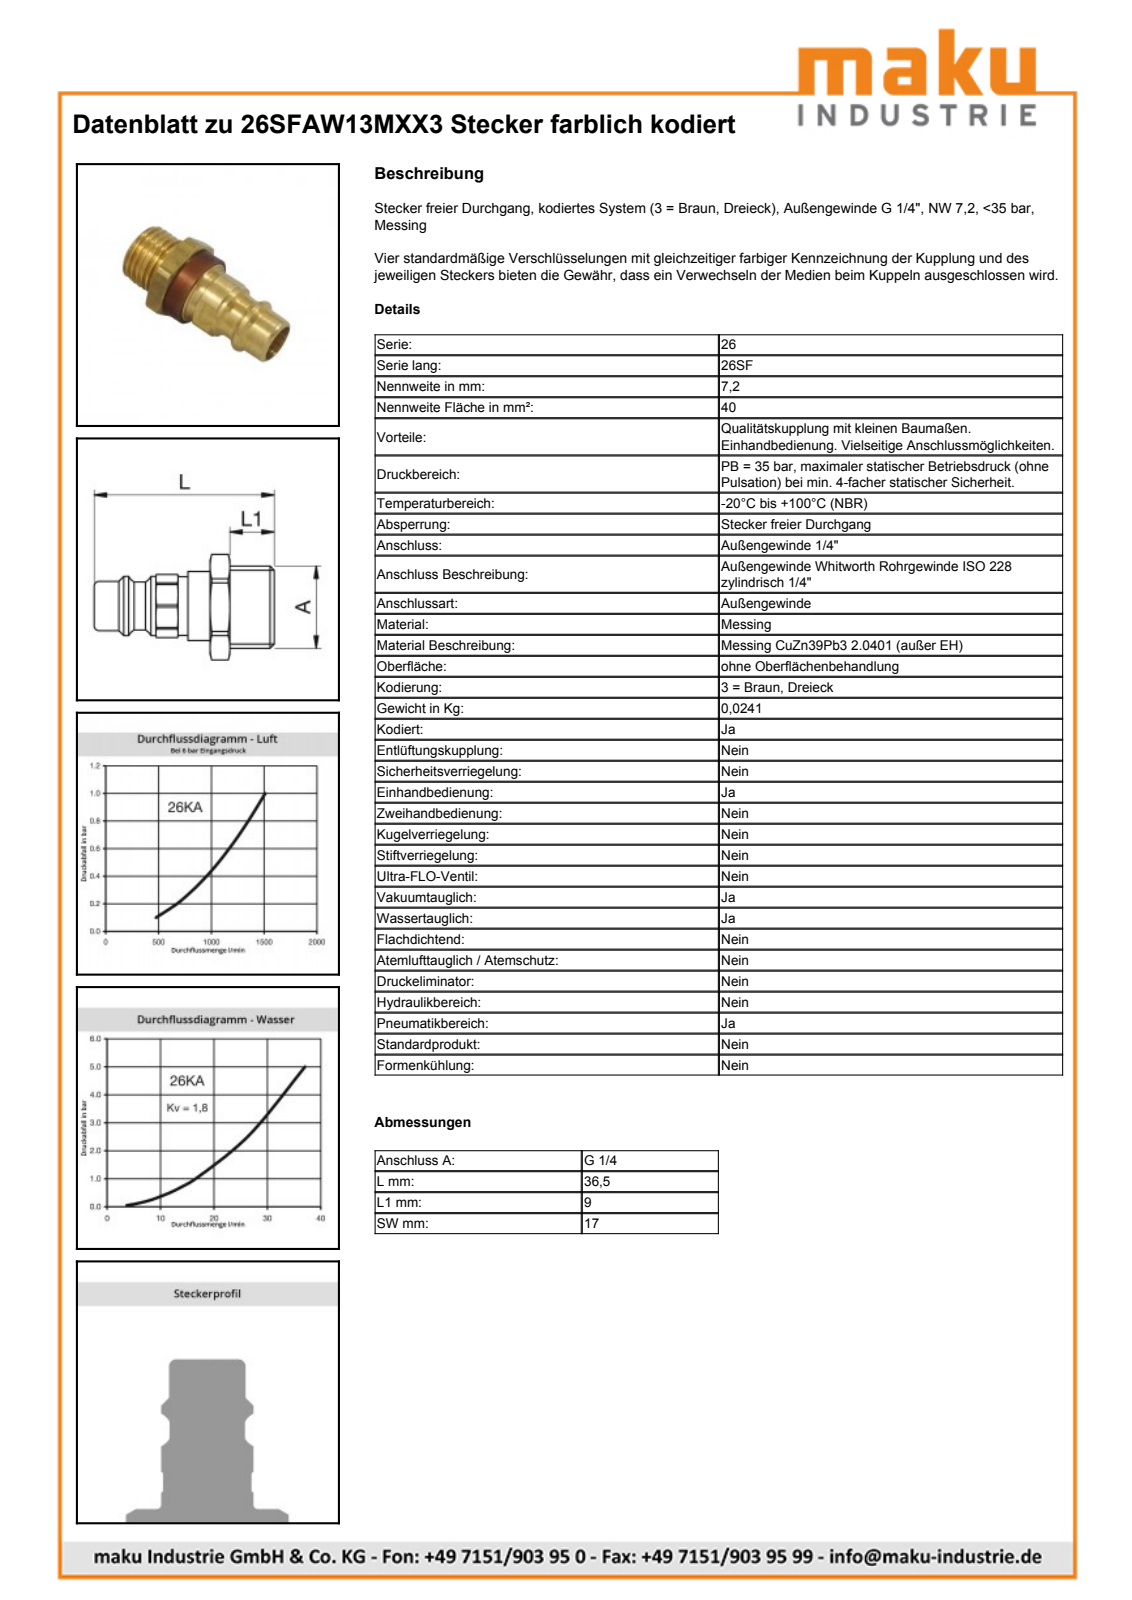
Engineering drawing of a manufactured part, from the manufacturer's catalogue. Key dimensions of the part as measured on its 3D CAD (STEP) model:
Part name (STEP PRODUCT): D103783; D103782; D103012
STEP written by: Autodesk Inventor 2011 (AUTOMOTIVE_DESIGN)
Units: millimetres
Bodies: 2 solids, 62 faces (16 planar, 20 cylindrical, 26 other)
Overall size (bounding box): 36.5 × 19.15 × 17
Volume: 3 158 mm³ · Surface area: 3 211 mm²
Round holes (diameter × count): ⌀7.85 ×1, ⌀13.85 ×1, ⌀14.05 ×1
Round bosses / shafts (diameter × count): ⌀15.5 ×1, ⌀14 ×1, ⌀13.16 ×1, ⌀12 ×1, ⌀11.9 ×1, ⌀10 ×1, ⌀9.75 ×1
Partial cylindrical surfaces — rounded edges, fillets, slot ends (radius × count): R6.6 ×1, R9.57 ×1
Main face-to-face distances: 17, 4, 14.8, 2.2, 4.5, 8.5, 17.5, 13, 9, 4.2
